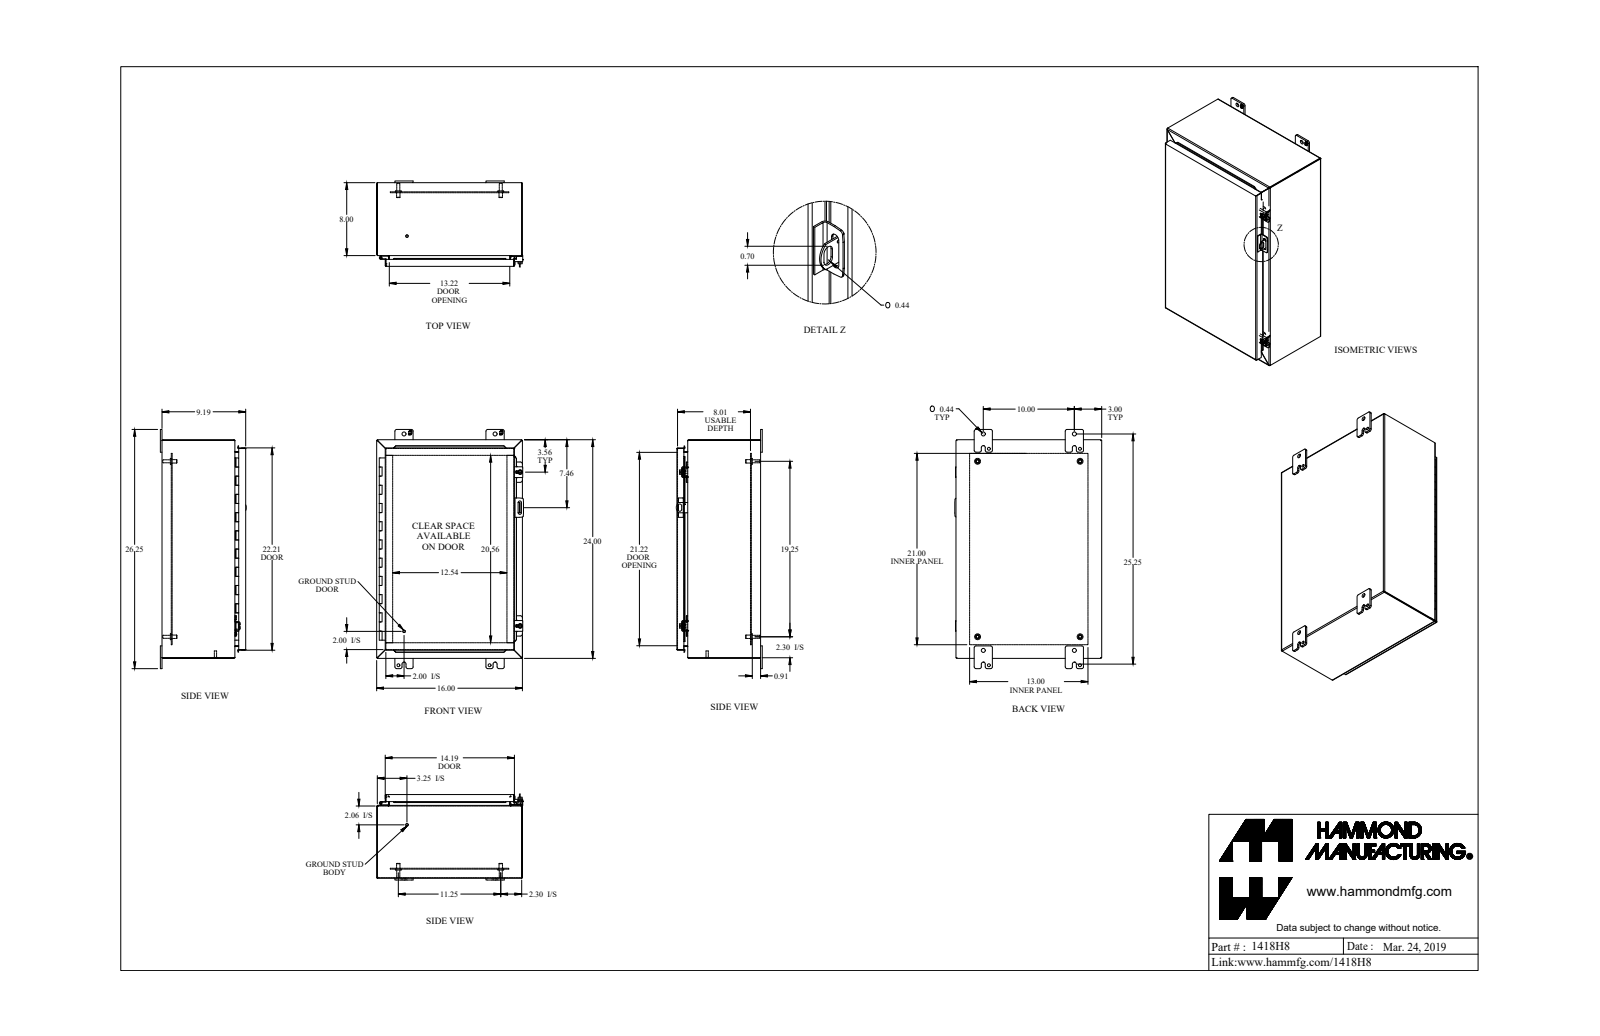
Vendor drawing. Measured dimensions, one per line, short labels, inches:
name: 1418H8
written by: SolidWorks 2019 (AUTOMOTIVE_DESIGN)
unit: in
bodies: 38 solids, 996 faces (683 planar, 259 cylindrical, 54 other)
size: 26.25 × 16.125 × 9.437
volume: 157.9 in³; area: 4 113 in²
holes: 4× ⌀0.313, 4× ⌀0.437, 4× ⌀0.5, 2× ⌀0.213, 2× ⌀0.265, 2× ⌀0.307, 2× ⌀0.375, 2× ⌀0.445, 1× ⌀0.125, 1× ⌀0.187
bosses: 4× ⌀0.65, 4× ⌀0.375, 4× ⌀0.33, 2× ⌀1, 2× ⌀0.5, 2× ⌀0.39, 2× ⌀0.281, 2× ⌀0.25
rounds: 26× R0.188, 20× R0.036, 20× R0.108, 13× R0.048, 13× R0.143, 8× R0.007, 8× R0.045, 8× R0.079
face distances: 0.072, 9.113, 9.041, 15.928, 0.937, 9.185, 1.009, 0.095, 8.081, 8.009
hole spacings: 10, 1.735, 23.75, 25.769, 1.625, 3.065, 10.492, 10.73
